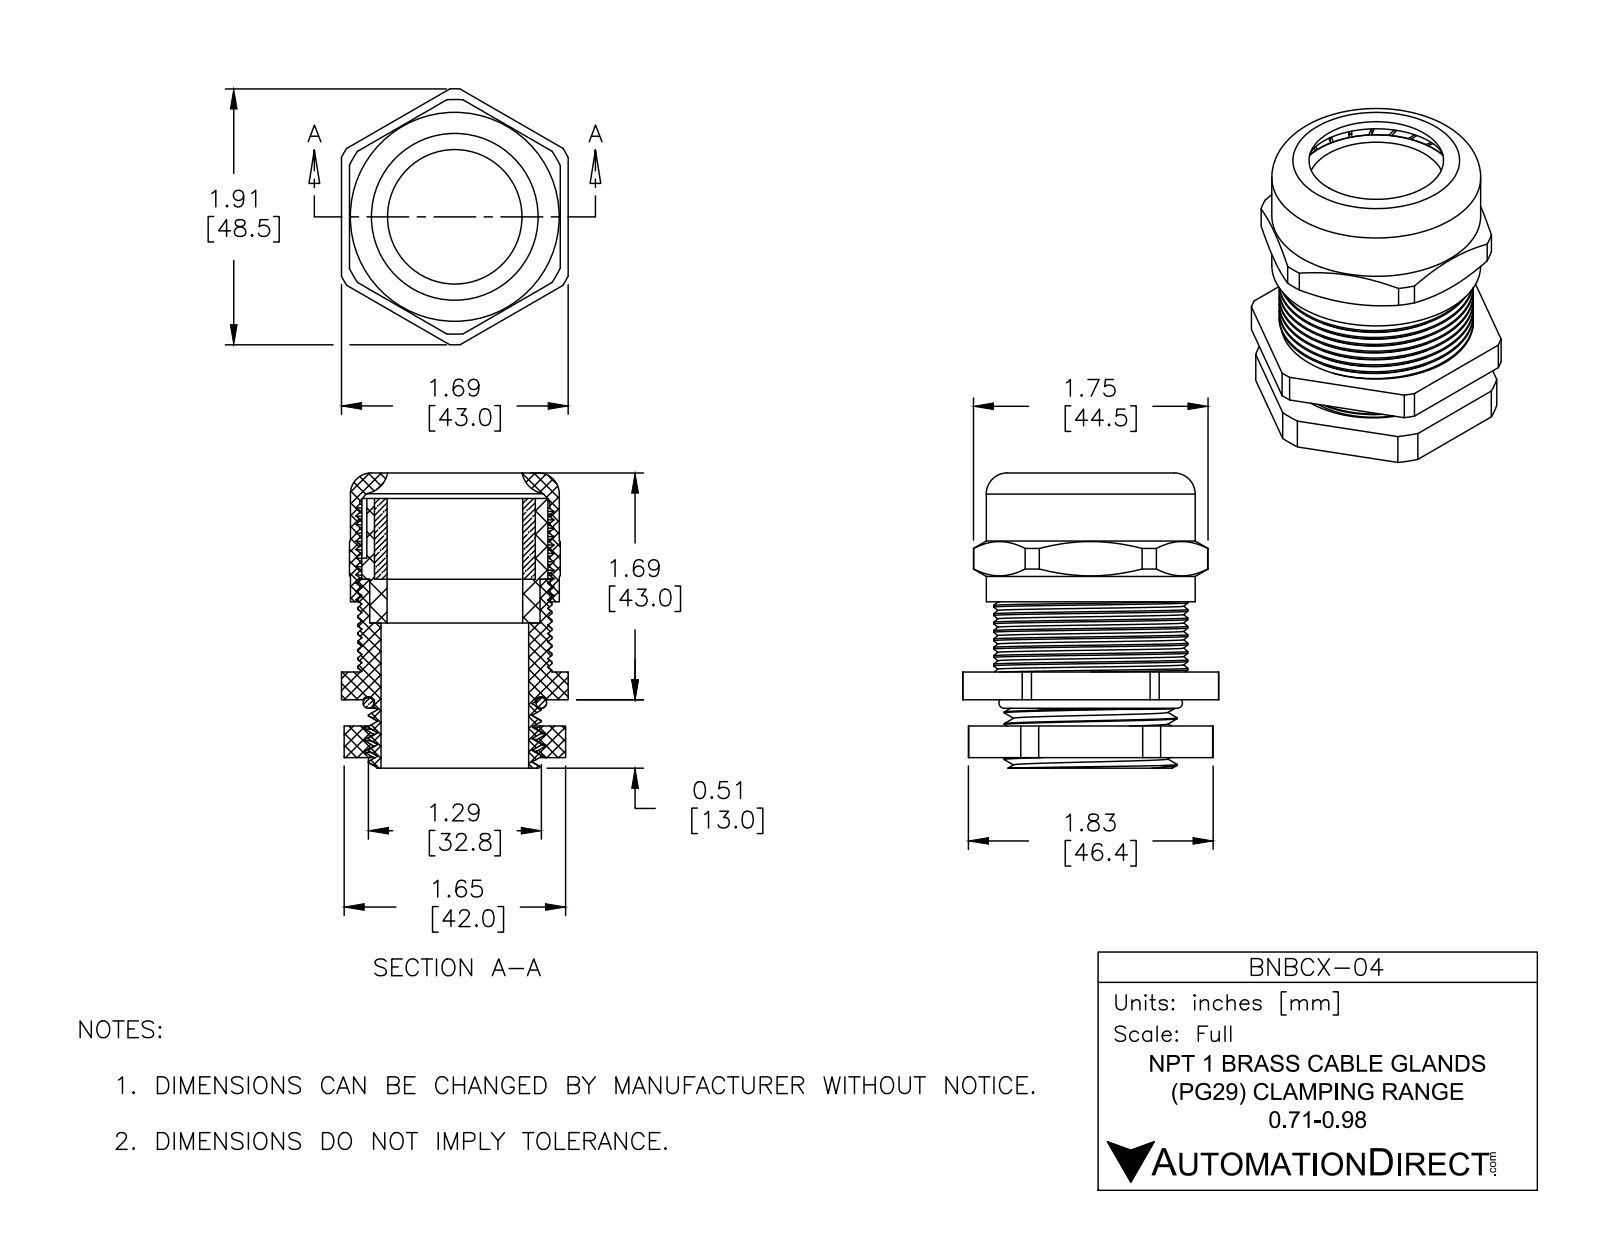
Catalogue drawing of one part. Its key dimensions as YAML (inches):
part_name: "BNBCX-04"
step_written_by: "SolidWorks 2015 (CONFIG_CONTROL_DESIGN)"
units: inches
bodies: {solids: 6, faces: 273, planar: 134, cylindrical: 106, other: 33}
overall_size: [2.203, 1.91, 1.692]
volume: 1.995
surface_area: 51.15
round_holes:
  - {diameter: 1.012, count: 1}
  - {diameter: 1.102, count: 1}
  - {diameter: 1.201, count: 1}
  - {diameter: 1.221, count: 1}
  - {diameter: 1.272, count: 1}
  - {diameter: 1.419, count: 1}
round_bosses_or_shafts:
  - {diameter: 1.559, count: 1}
  - {diameter: 1.449, count: 1}
  - {diameter: 1.39, count: 1}
  - {diameter: 1.291, count: 1}
partial_cylinders:
  - {radius: 0.876, count: 1}
  - {radius: 0.913, count: 1}
  - {radius: 0.955, count: 1}
face_to_face_distances: [0.019, 1.673, 0.02, 1.332, 0.236, 1.096, 0.432, 0.196, 0.9, 0.059]
